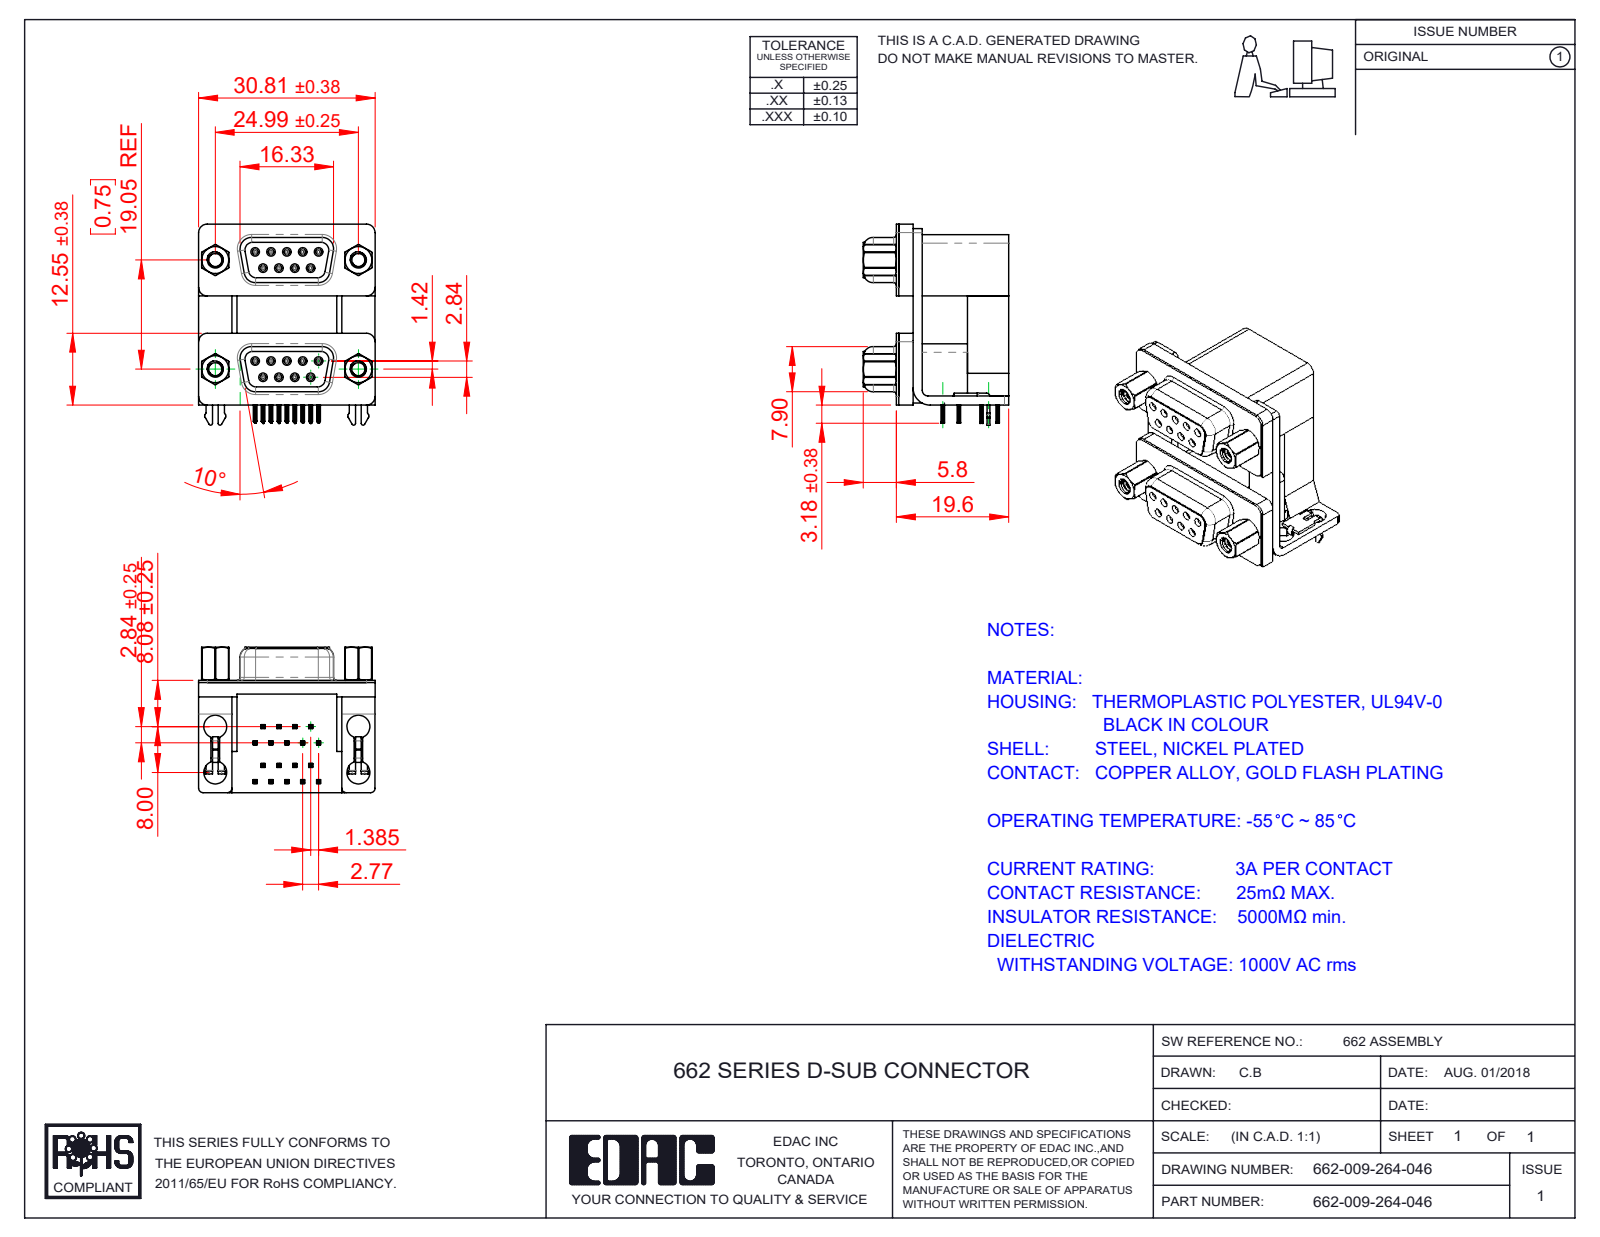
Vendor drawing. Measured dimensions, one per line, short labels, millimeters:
name: 662 Housing Upper_09 Contacts M; 662 Housing Spacer_09 Contacts M; 662-009-264-046; 662 Mounting Bracket_2ProngM (+8 more)
written by: SolidWorks 2020 (CONFIG_CONTROL_DESIGN)
unit: mm
bodies: 35 solids, 3470 faces (1496 planar, 970 cylindrical, 1004 other)
size: 35.1 × 30.81 × 25.4
volume: 11 717 mm³; area: 14 341 mm²
holes: 18× ⌀0.8, 18× ⌀0.9, 8× ⌀4, 4× ⌀2.26, 4× ⌀2.29, 4× ⌀3.5, 4× ⌀4.8, 4× ⌀5
bosses: 18× ⌀1.2, 4× ⌀4.9, 4× ⌀4.75, 4× ⌀3.9, 4× ⌀2.79
rounds: 145× R0.1, 72× R0.15, 36× R0.35, 18× R0.34, 16× R1.35, 12× R0.5, 12× R1.5, 10× R0.75
face distances: 0.4, 2.5, 16.7, 19.2, 19.05, 2.9, 12, 12.4, 19.6, 7.2
hole spacings: 3.16, 19.25, 2.77, 19.05, 19.84, 21.93, 5.54, 22.28
